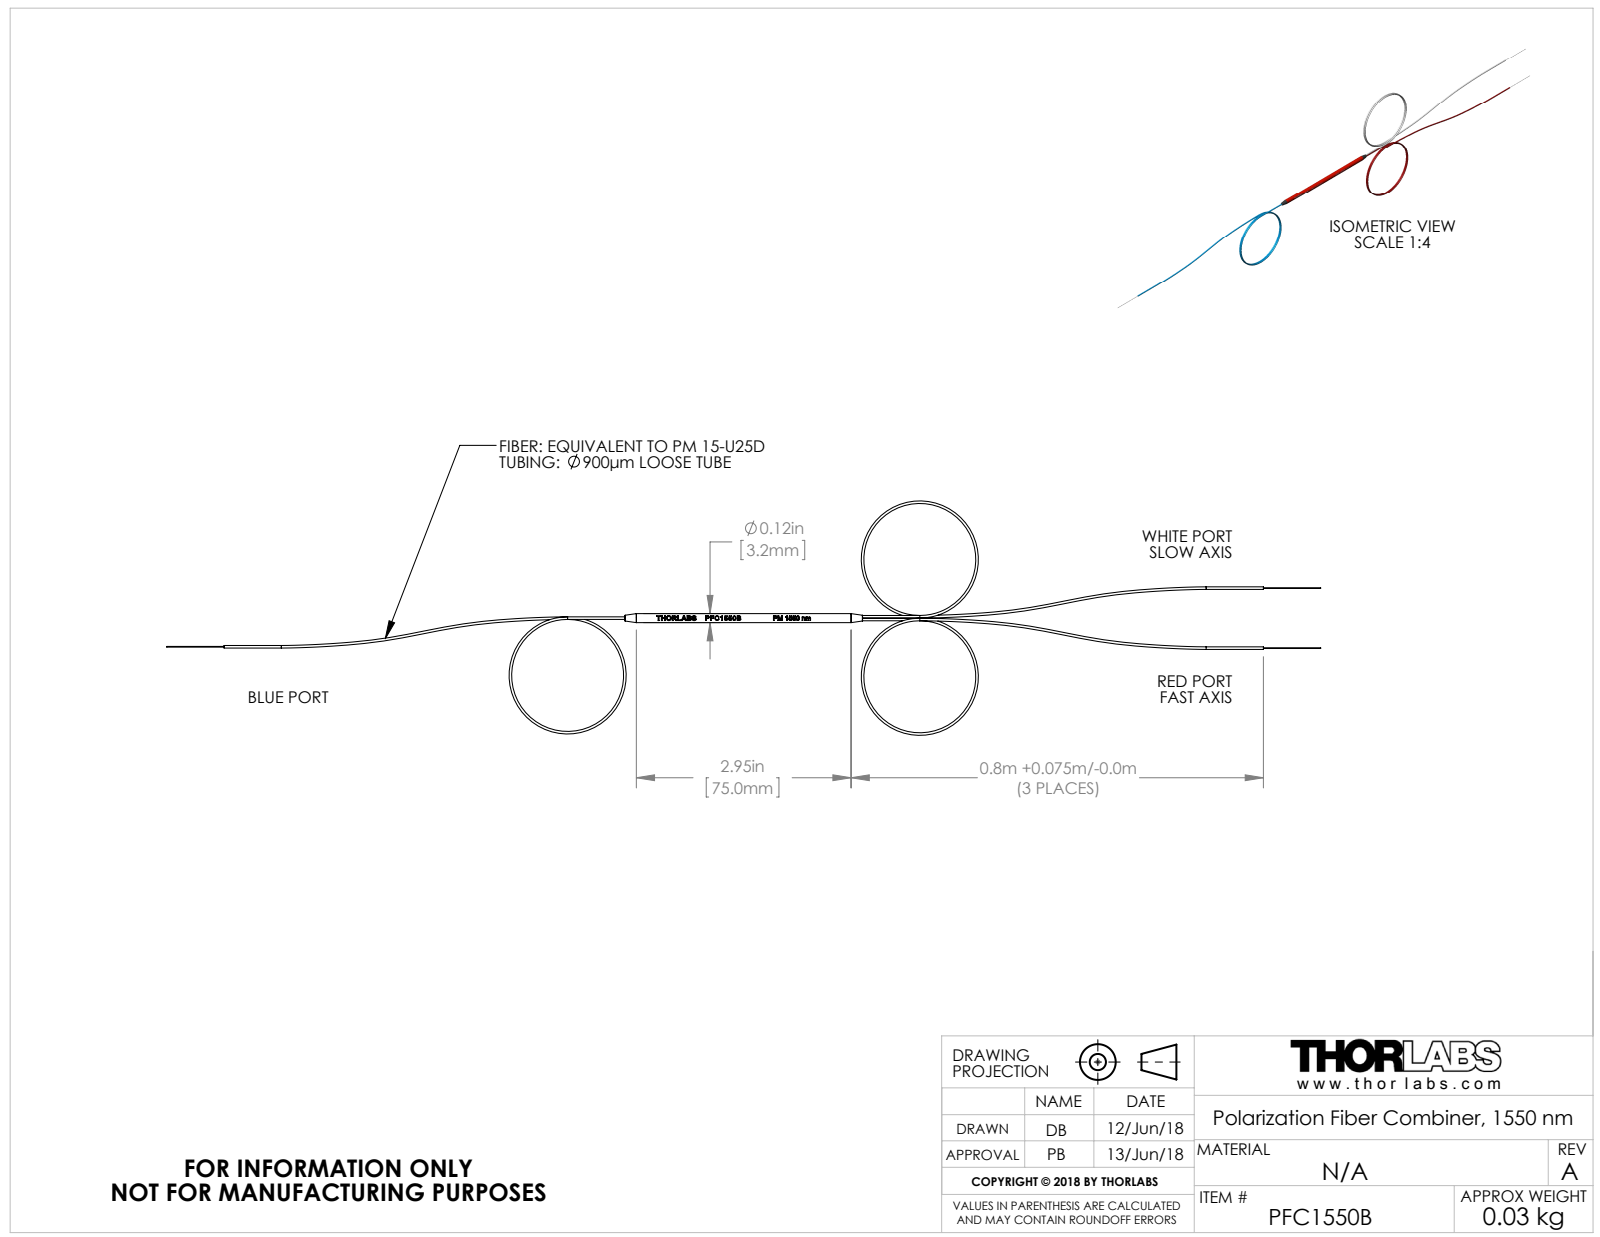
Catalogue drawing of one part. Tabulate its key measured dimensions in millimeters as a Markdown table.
| quantity | value |
| --- | --- |
| part name | PANDA 1550_60; LA000PLBTTB; DWG1540; DWG1553 (+8 more) |
| STEP written by | SolidWorks 2014 (CONFIG_CONTROL_DESIGN) |
| units | millimeters |
| bodies | 14 solids, 253 faces (41 planar, 152 cylindrical, 60 other) |
| overall size | 403 × 81.85 × 5.1 |
| volume | 838 mm³ |
| surface area | 7 397 mm² |
| round holes (diameter × count) | 0.5 × 6, 0.95 × 3, 2.69 × 1 |
| round bosses / shafts (diameter × count) | 0.9 × 6, 0.25 × 5, 3.15 × 1, 2.5 × 1 |
| partial cylindrical surfaces (radius × count) | 0.45 × 2, 1 × 1 |
| main face-to-face distances | 3, 69, 72, 6, 66, 75, 63, 60, 15, 54 |
| hole center spacings | 10.2, 0.47, 0.48, 0.95, 4.03, 9.74, 10.24, 10.66 |
